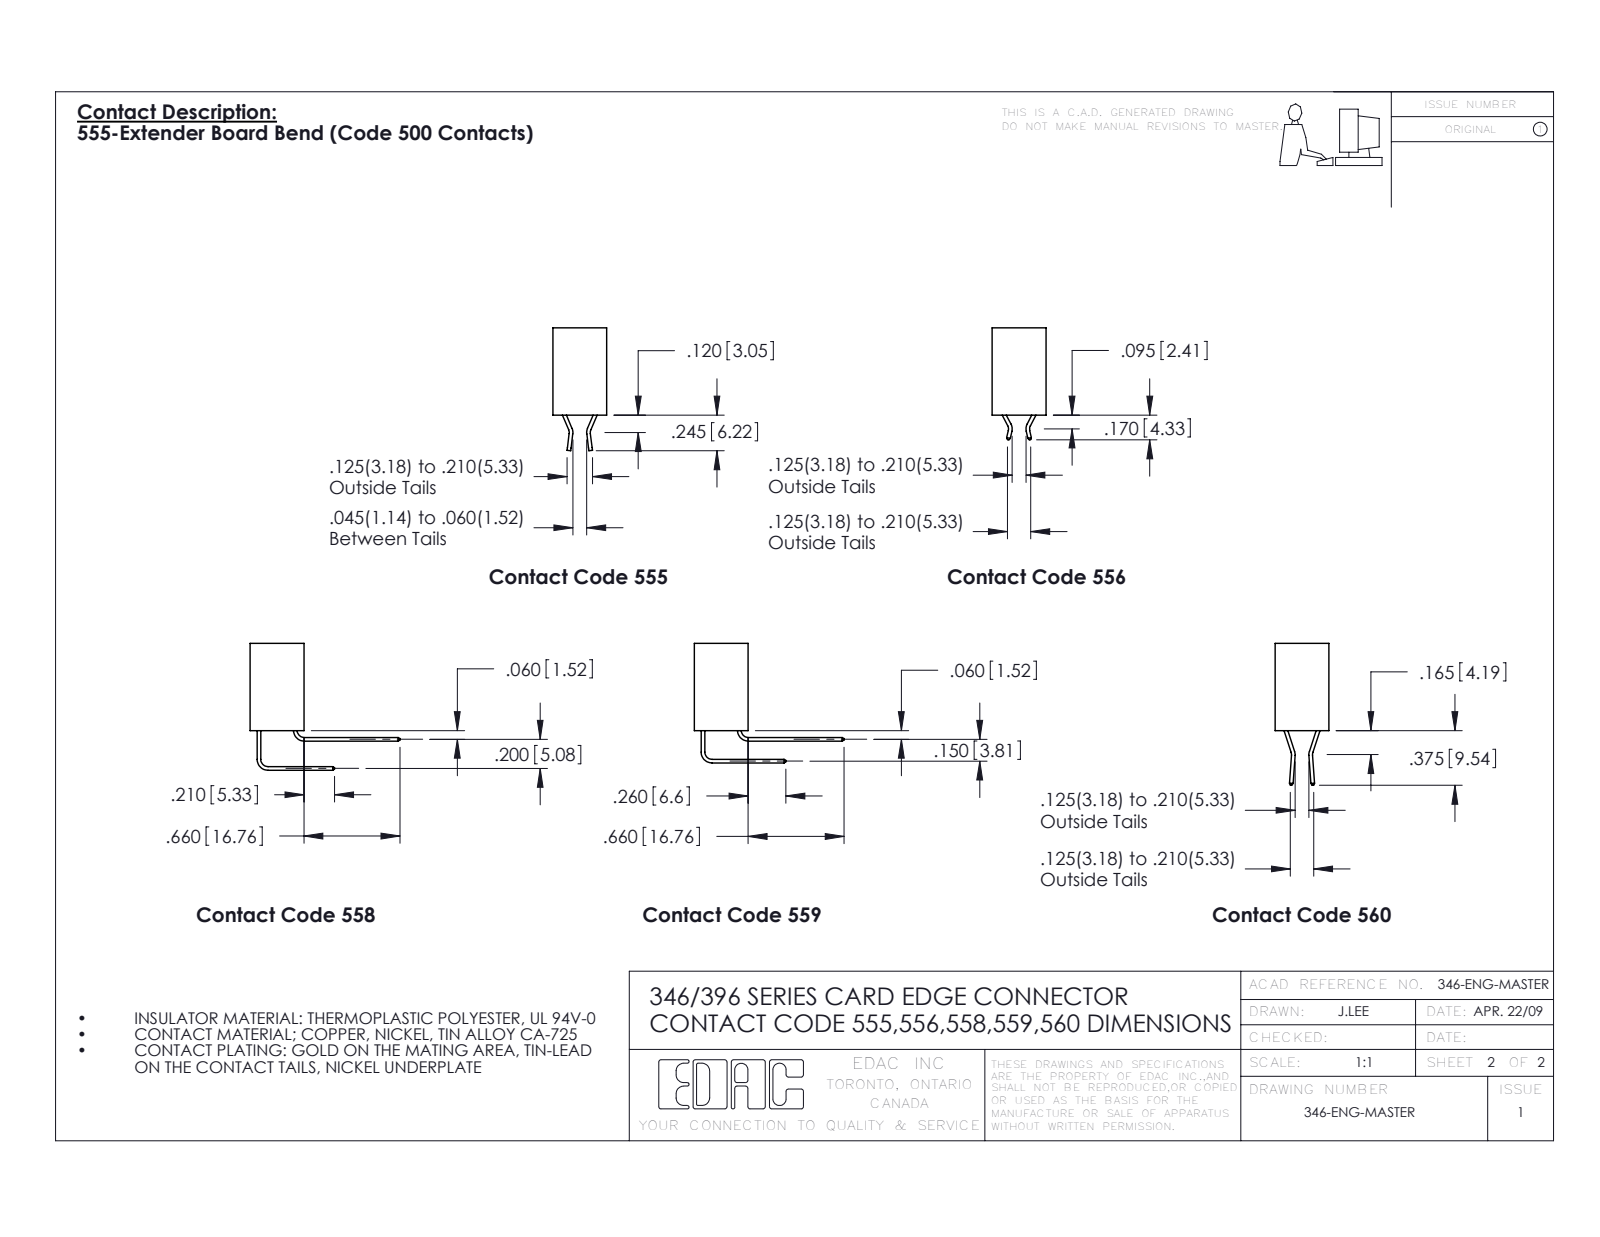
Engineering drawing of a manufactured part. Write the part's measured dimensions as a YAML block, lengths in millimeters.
part_name: "396-025-559-101; 345-292-001_558 559 Tail - 1; 346 Part_No Mounting Lugs"
step_written_by: "SolidWorks 2016 (CONFIG_CONTROL_DESIGN)"
units: millimeters
bodies: {solids: 26, faces: 1614, planar: 1122, cylindrical: 492, other: 0}
overall_size: [86.6, 26.2, 17.1]
volume: 8800
surface_area: 11390
round_holes:
  - {diameter: 1.6, count: 1}
partial_cylinders:
  - {radius: 0.2, count: 50}
  - {radius: 0.3, count: 22}
  - {radius: 0.2, count: 6}
  - {radius: 0.8, count: 6}
  - {radius: 0.7, count: 3}
  - {radius: 0.8, count: 2}
  - {radius: 1, count: 2}
  - {radius: 0.4, count: 1}
face_to_face_distances: [1.2, 8.2, 9.4, 6.4, 0.6, 1.8, 3.8, 5.6, 2.5, 4.4]
